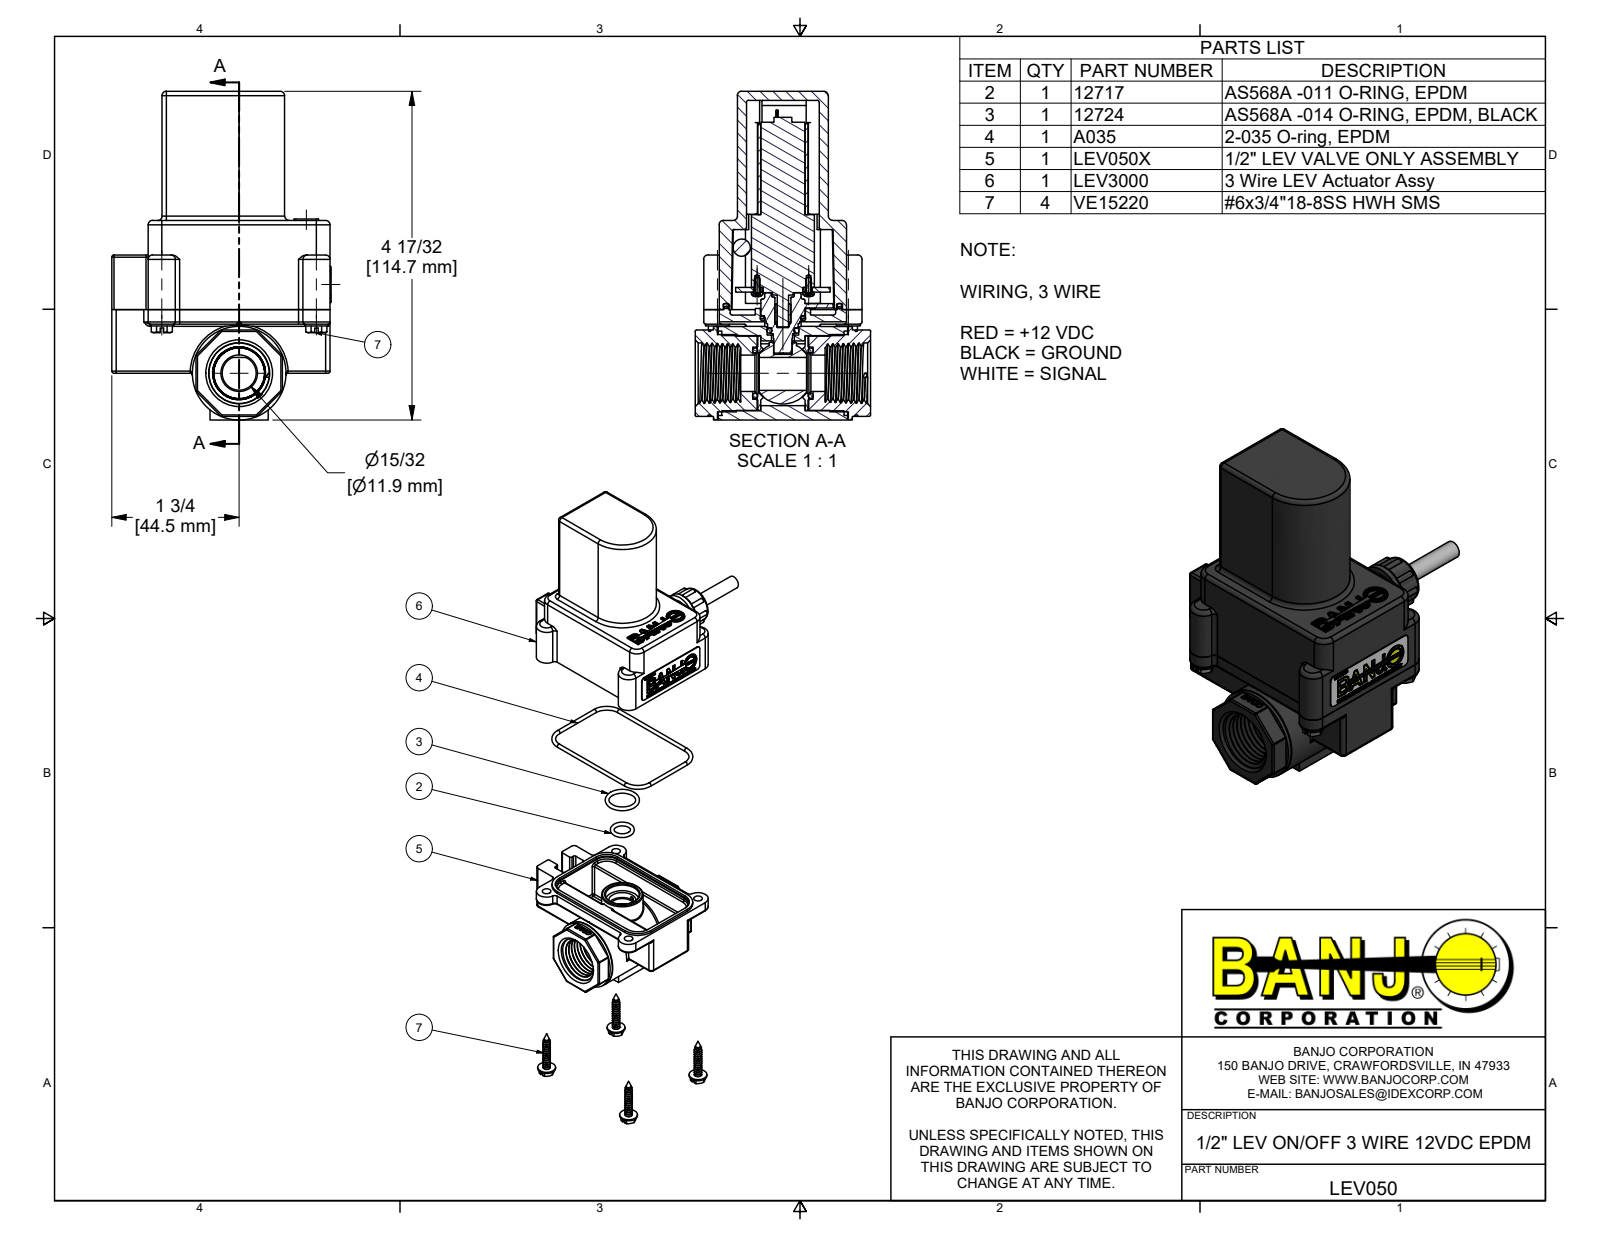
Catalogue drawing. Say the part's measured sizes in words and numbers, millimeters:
The part is named "LEV050; 12724; 12717; A035_LEV_Fit (+8 more)". Its 3-D file was written by "Autodesk Inventor 2022 (AUTOMOTIVE_DESIGN)". It is 32 solids with 3168 faces: 1492 planar, 711 cylindrical and 965 other. Overall it measures 114.8 by 90.7 by 76.5 millimeters. Its volume is 151 600 cubic millimeters and its surface area 97 740 square millimeters. Round holes: 8 of diameter 0.9, 4 of diameter 1.6, 4 of diameter 2.4, 4 of diameter 2.8, 4 of diameter 4.1, 4 of diameter 5.1, 2 of diameter 1.2, 2 of diameter 1.4, 2 of diameter 5.8, 2 of diameter 8.2, 1 of diameter 1.6, 1 of diameter 4.3. Round bosses or shafts: 4 of diameter 8.3, 4 of diameter 4, 4 of diameter 3.5, 4 of diameter 2, 4 of diameter 1.8, 4 of diameter 1.5, 4 of diameter 1.2, 2 of diameter 8.6. Partial cylindrical surfaces (rounded edges, fillets, slot ends): 102 of radius 0.8, 59 of radius 0.4, 28 of radius 1.5, 24 of radius 0.5, 16 of radius 0.3, 10 of radius 3.2, 8 of radius 1, 8 of radius 4.7. The main face-to-face distances are 3.2, 1.7, 34.9, 25.4, 9.5, 30, 38.1, 28.6, 3.2, 6.4. The hole center spacings are 2.5, 12.7, 21.7, 24.1, 25.1, 3.6, 9, 9.
